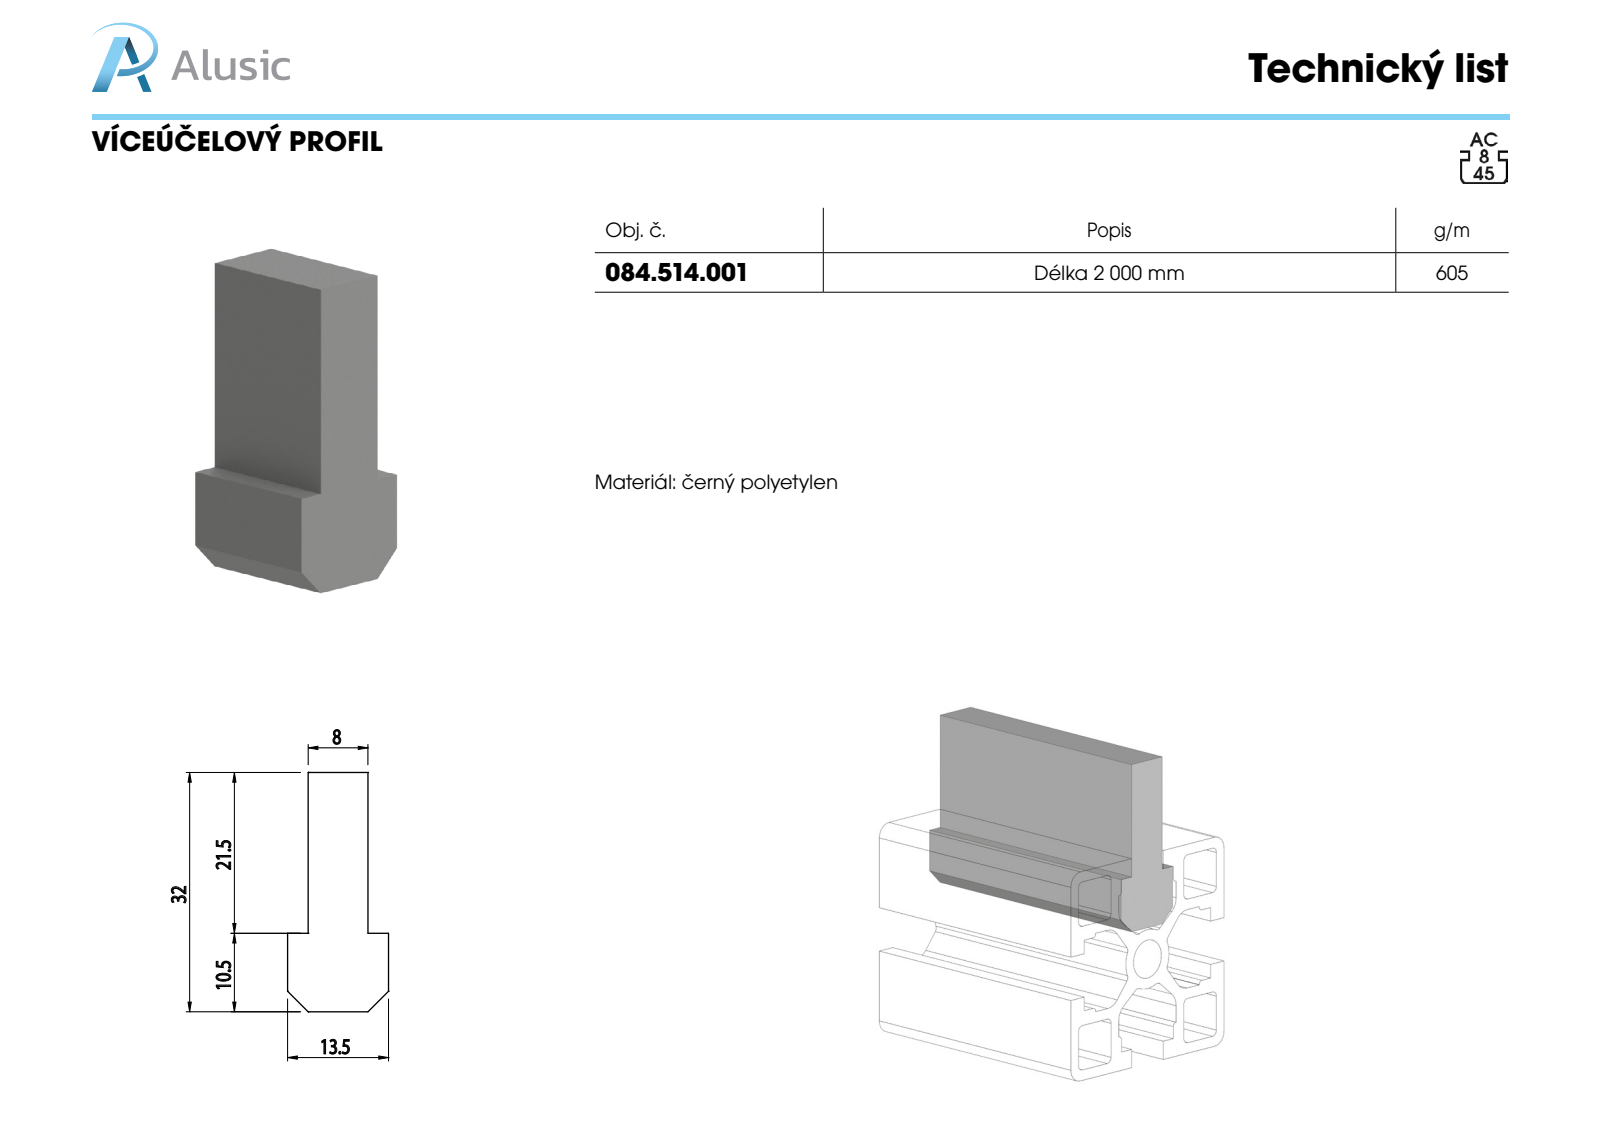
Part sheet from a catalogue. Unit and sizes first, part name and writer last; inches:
Units: inches
Overall size (bounding box): 3.937 × 1.26 × 0.531
Main face-to-face distances: 0.315, 0.108, 0.423, 1.26, 0.531, 0.413, 0.846, 3.937
Volume: 1.868 in³ · Surface area: 14.55 in²
Bodies: 1 solid, 12 faces (12 planar, 0 cylindrical, 0 other)
Part name (STEP PRODUCT): 084.514.001
STEP written by: SolidWorks 2011 (CONFIG_CONTROL_DESIGN)
